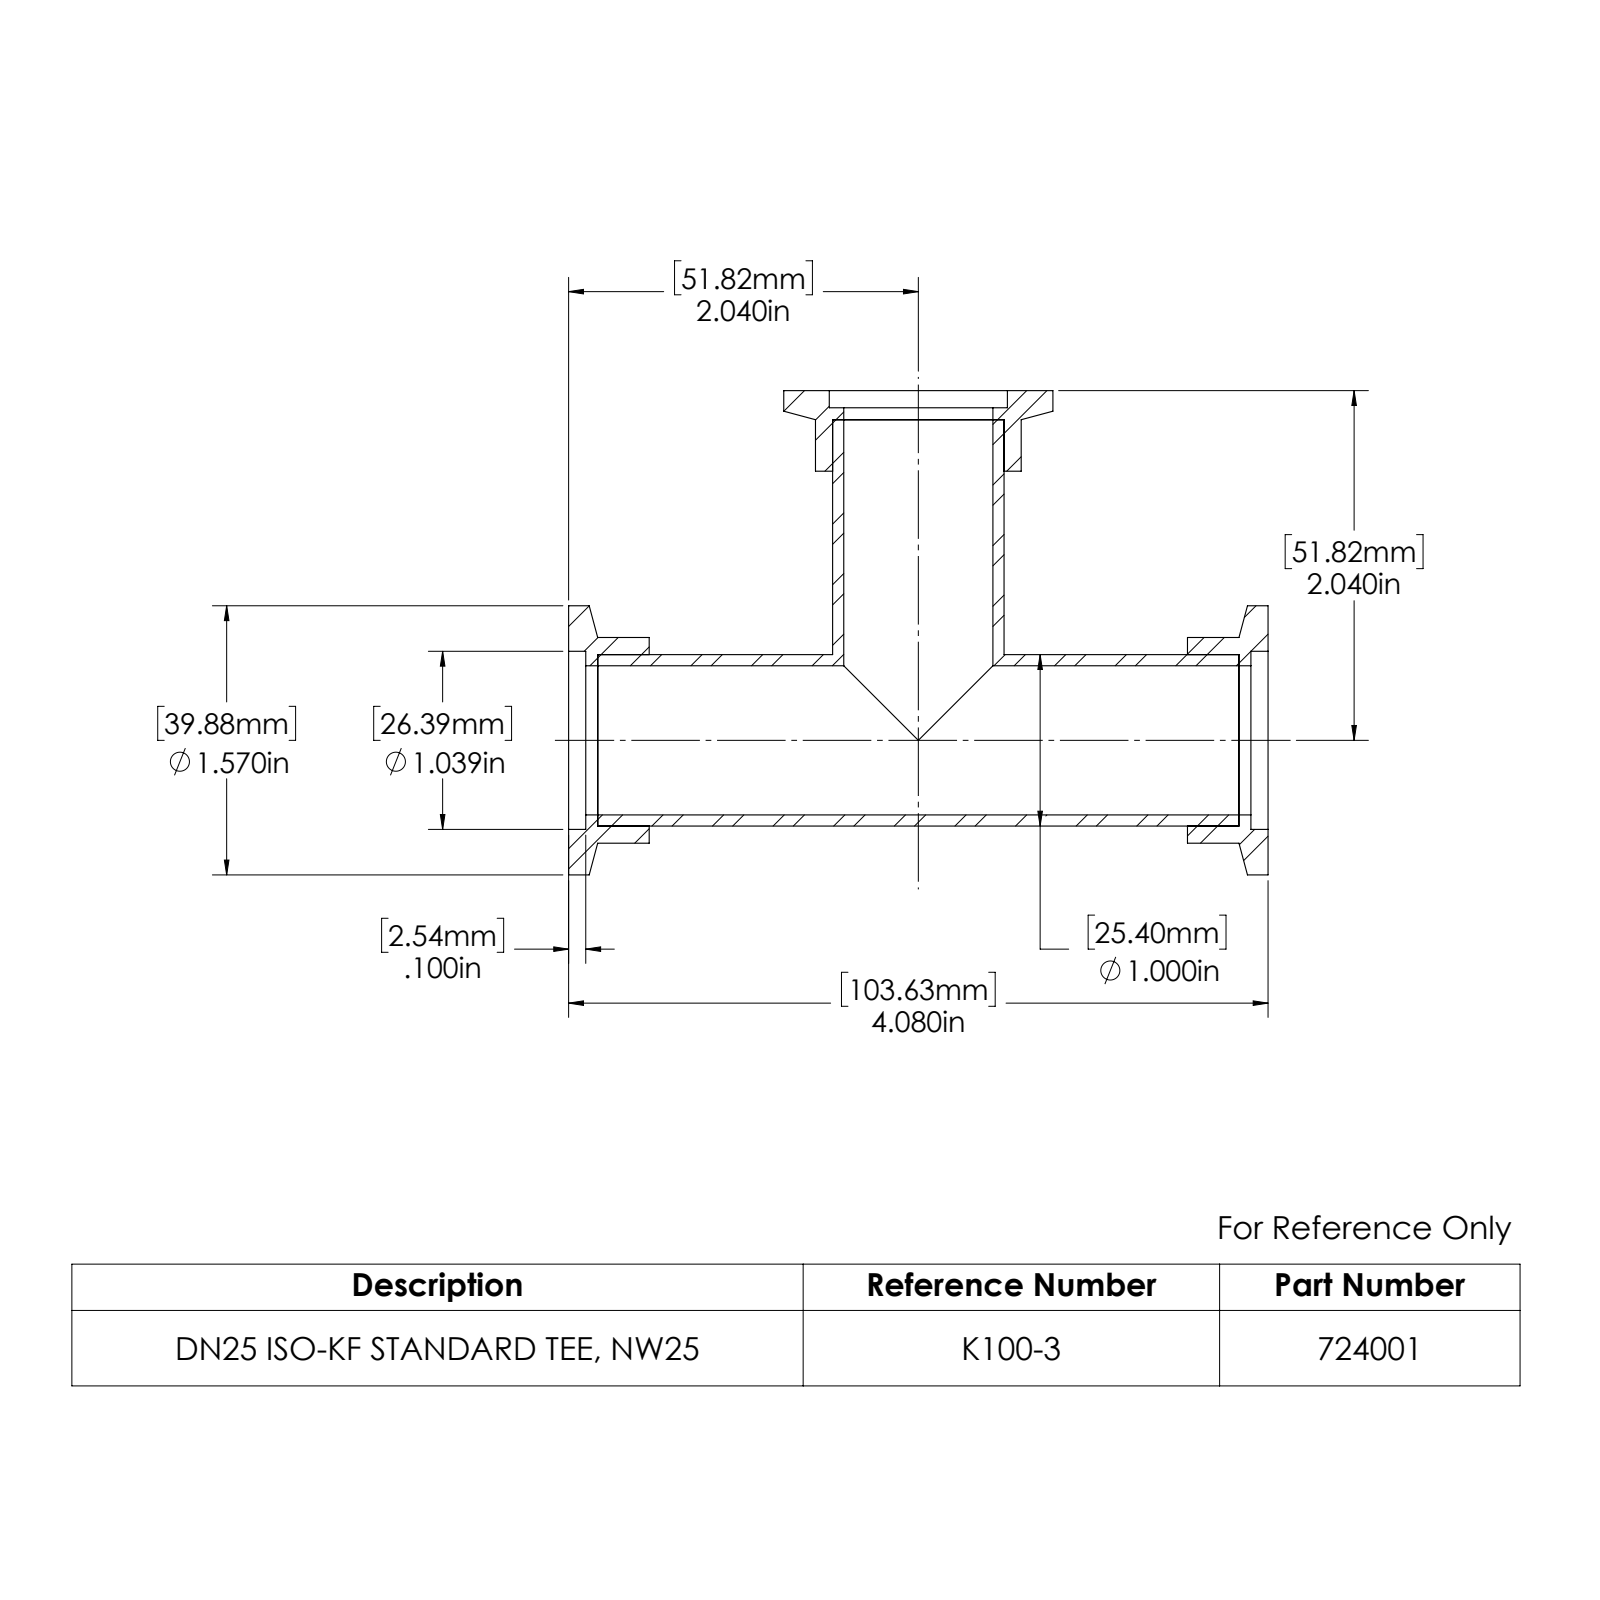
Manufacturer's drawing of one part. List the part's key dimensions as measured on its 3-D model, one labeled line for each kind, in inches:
Part name (STEP PRODUCT): 724001; 404501; 713002
STEP written by: SolidWorks 2022 (AUTOMOTIVE_DESIGN)
Units: inches
Bodies: 4 solids, 61 faces (15 planar, 40 cylindrical, 6 other)
Overall size (bounding box): 4.08 × 2.825 × 1.57
Volume: 1.813 in³ · Surface area: 47.7 in²
Round holes (diameter × count): ⌀0.87 ×2, ⌀1 ×2, ⌀1.039 ×2
Round bosses / shafts (diameter × count): ⌀1.57 ×2, ⌀1.2 ×2
Main face-to-face distances: 0.17, 4.08, 0.47, 0.3, 3.91, 0.1, 0.07, 0.37, 3.61, 3.44
